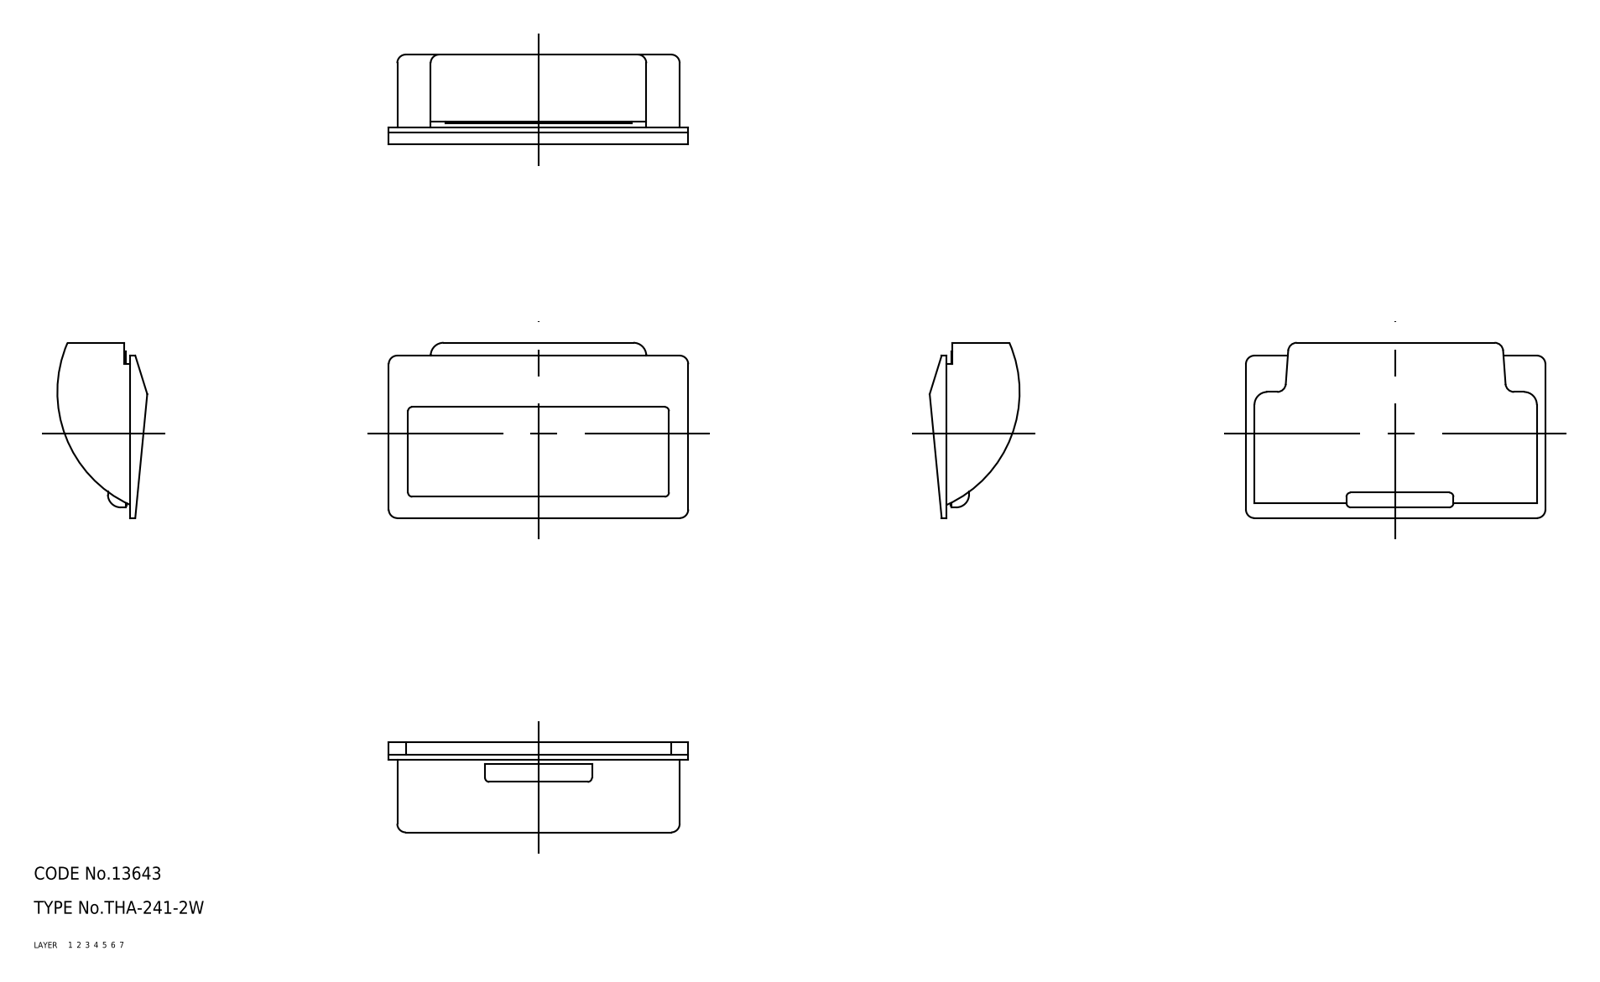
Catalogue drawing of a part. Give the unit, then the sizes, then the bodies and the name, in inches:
Units: inches
Overall size (bounding box): 2.756 × 1.614 × 0.827
Partial cylindrical surfaces — rounded edges, fillets, slot ends (radius × count): R0.039 ×17, R0.079 ×8, R0.118 ×3, R1.063 ×1, R1.142 ×1, R1.155 ×1
Main face-to-face distances: 0.079, 0.098, 0.512, 2.5, 0.335, 0.433, 2.165, 2.067, 2.598, 0.039
Volume: 0.877 in³ · Surface area: 18.2 in²
Bodies: 1 solid, 91 faces (39 planar, 32 cylindrical, 20 other)
Part name (STEP PRODUCT): pull; THA_241_2W
STEP written by: SolidWorks 2015 (AUTOMOTIVE_DESIGN)
